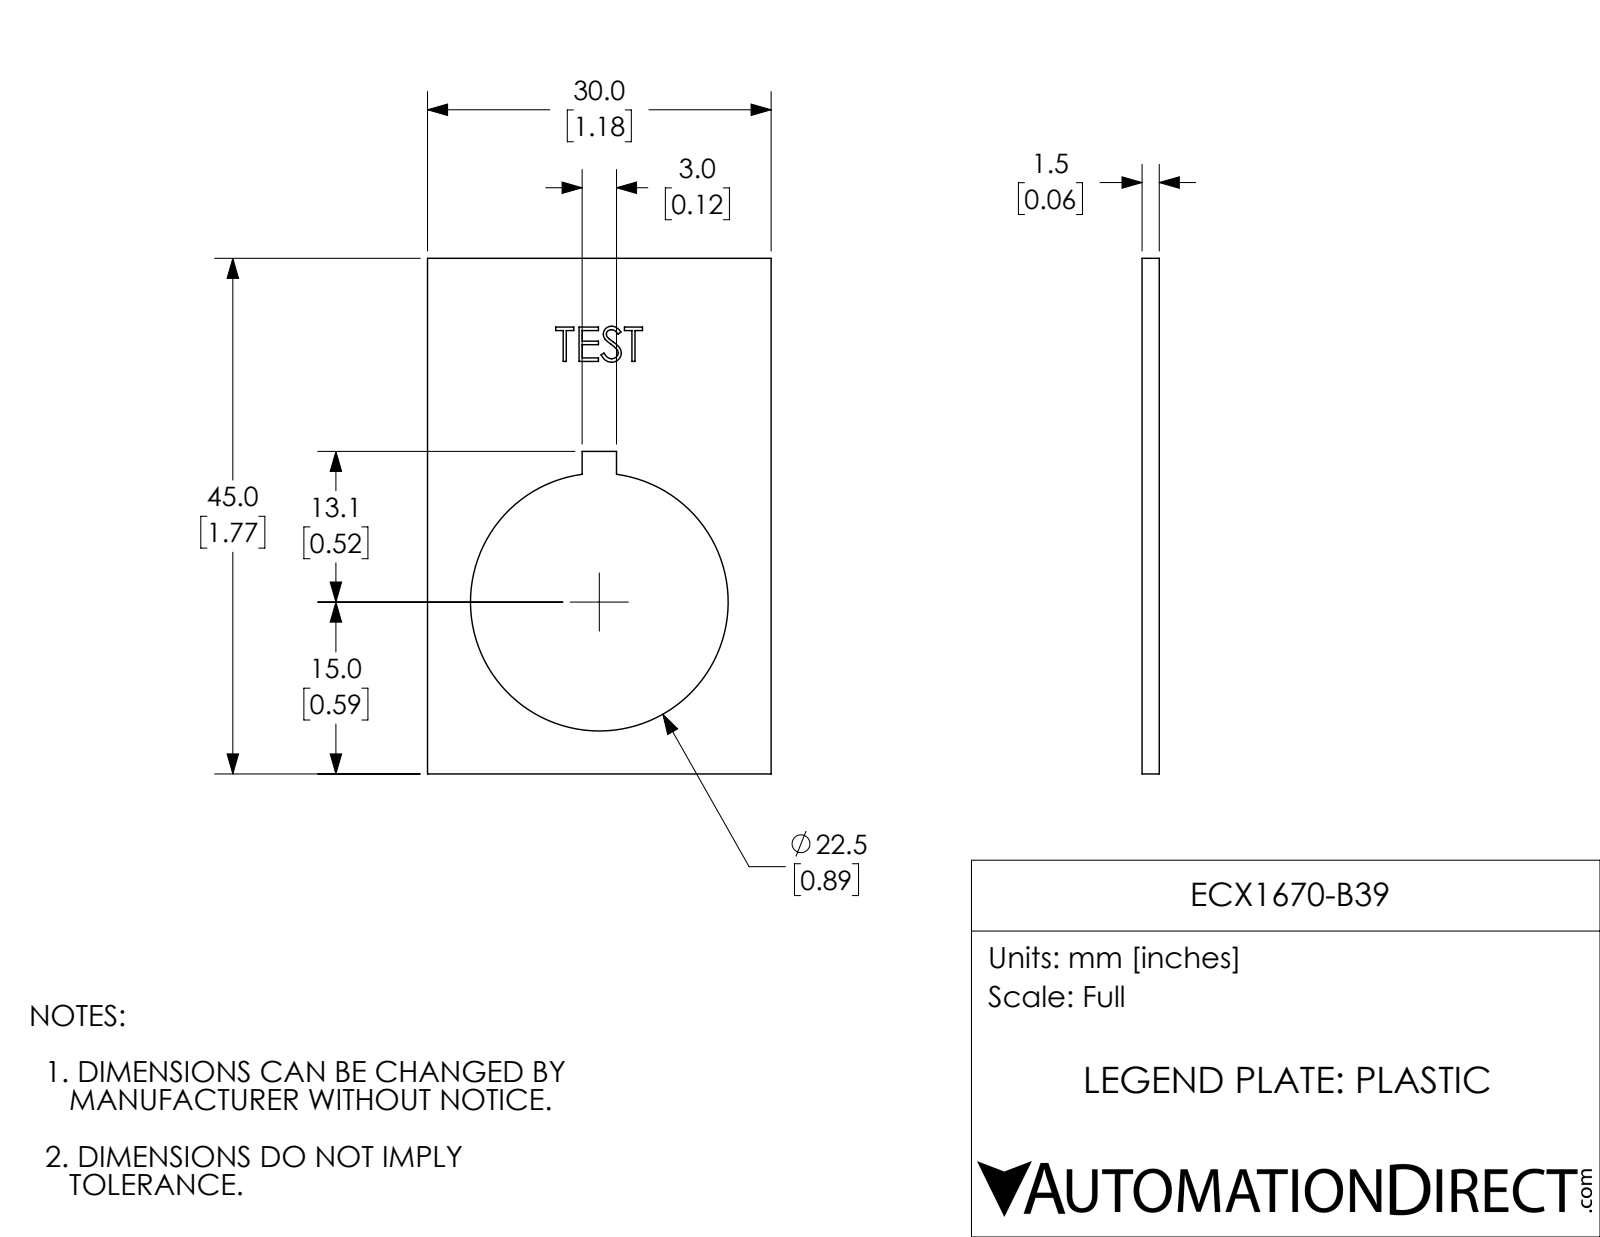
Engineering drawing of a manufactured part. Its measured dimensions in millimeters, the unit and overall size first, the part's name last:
Units: millimetres
Overall size (bounding box): 45 × 30 × 1.5
Round holes (diameter × count): ⌀22.5 ×1
Main face-to-face distances: 1.5, 30, 45, 1.5, 13.5, 16.5, 28.1, 16.8, 3, 6
Volume: 1 400 mm³ · Surface area: 2 232 mm²
Bodies: 1 solid, 61 faces (43 planar, 3 cylindrical, 15 other)
Part name (STEP PRODUCT): ECX1670-B39
STEP written by: SolidWorks 2017 (AUTOMOTIVE_DESIGN)
